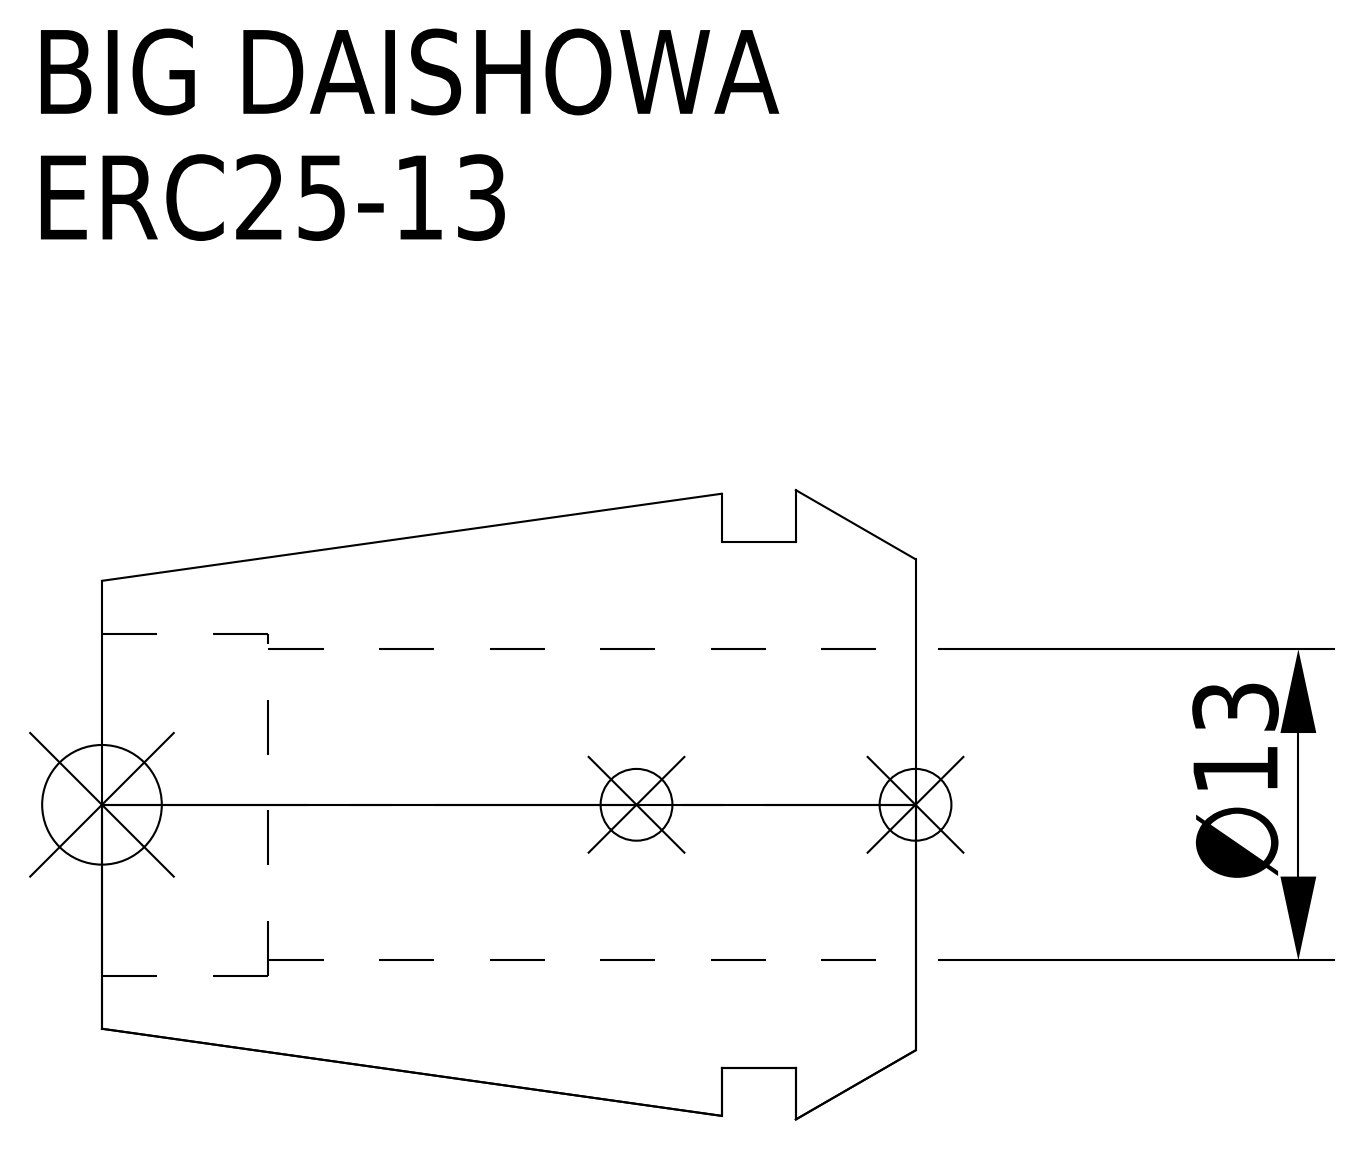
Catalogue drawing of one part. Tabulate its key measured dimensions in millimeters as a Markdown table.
| quantity | value |
| --- | --- |
| part name | ERC25-13 |
| STEP written by | CREO PARAMETRIC BY PTC INC, 2016380 (AUTOMOTIVE_DESIGN) |
| units | millimeters |
| bodies | 1 solid, 15 faces (5 planar, 6 cylindrical, 4 other) |
| overall size | 34 × 26.3 × 26.3 |
| volume | 8 896 mm³ |
| surface area | 4 548 mm² |
| round holes (diameter × count) | 13 × 1, 14.3 × 1 |
| round bosses / shafts (diameter × count) | 22 × 1 |
| main face-to-face distances | 5, 8.1, 3.1, 34, 29, 25.9, 27.04, 22.04, 18.94, 6.96 |
